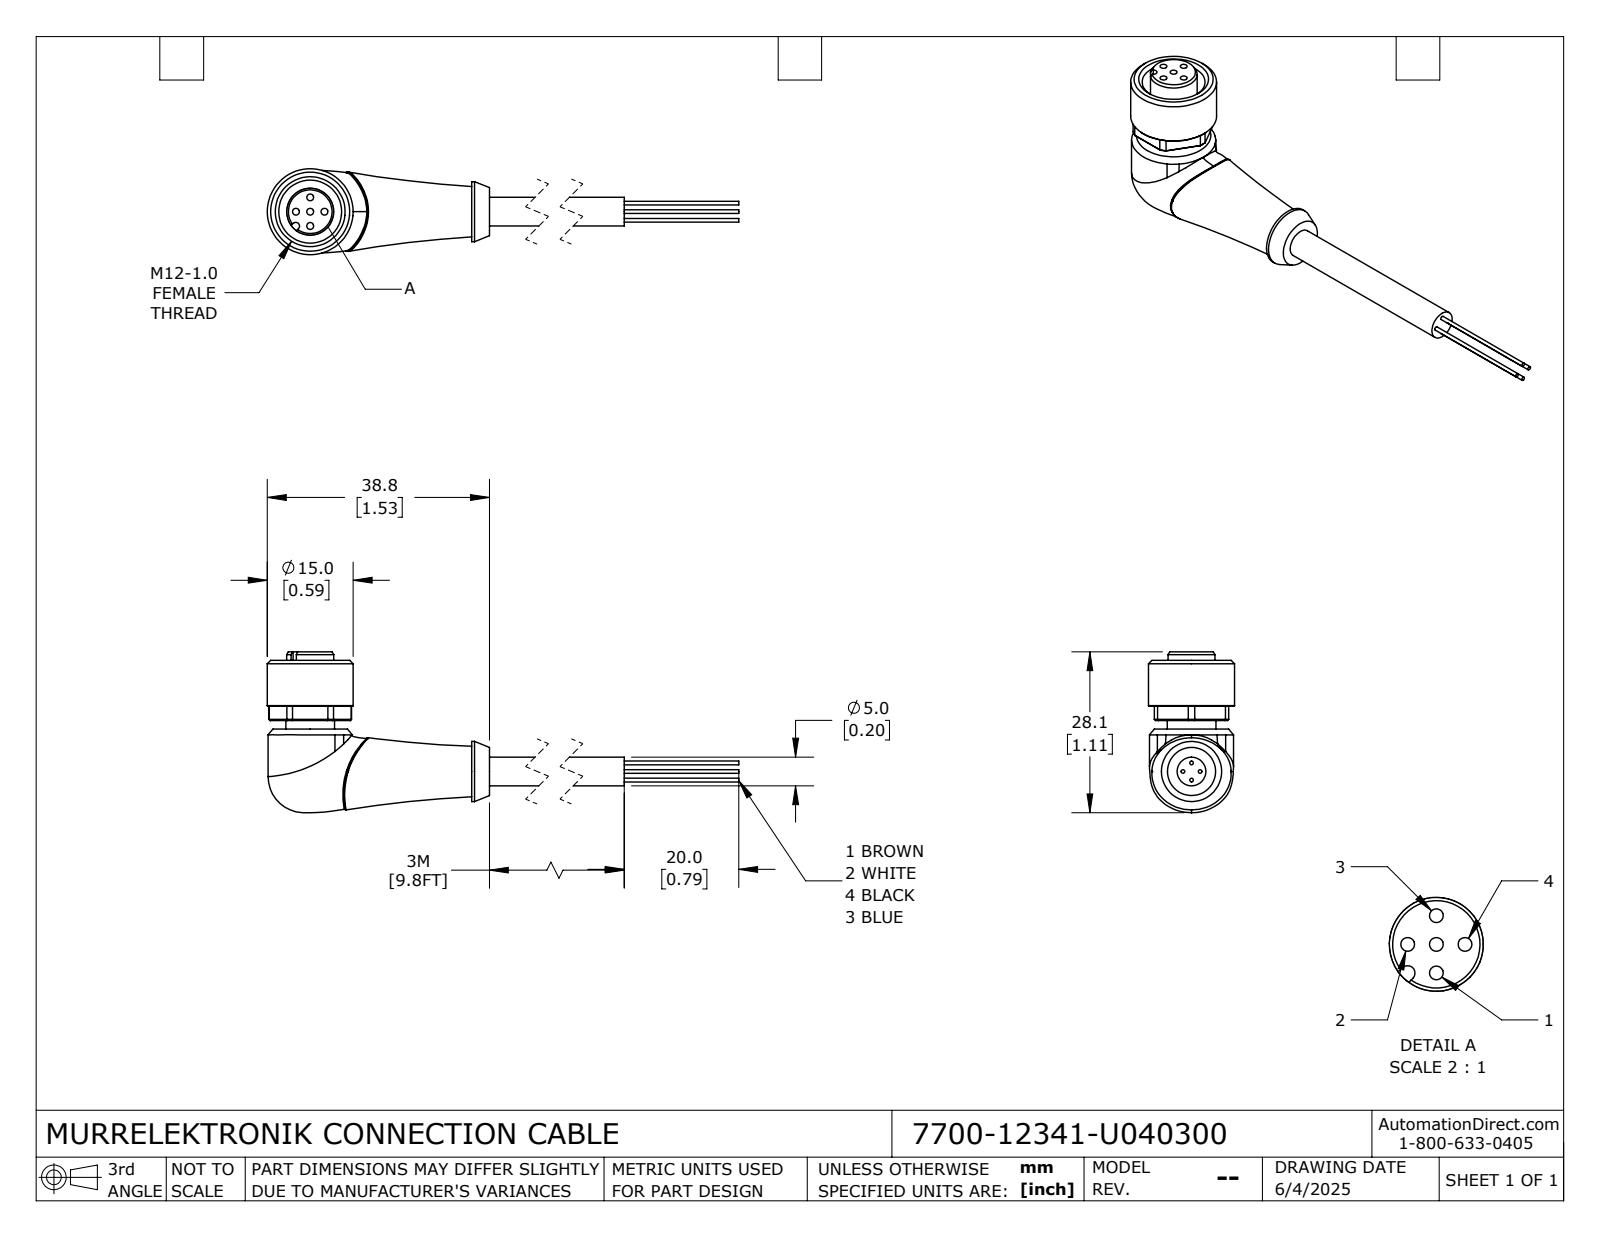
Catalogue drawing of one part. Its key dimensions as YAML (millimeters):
part_name: "7700-12341-U040300"
step_written_by: "SolidWorks 2024 (CONFIG_CONTROL_DESIGN)"
units: millimeters
bodies: {solids: 1, faces: 109, planar: 33, cylindrical: 39, other: 37}
overall_size: [93.8, 28.11, 15]
volume: 6692
surface_area: 3745
round_holes:
  - {diameter: 1.2, count: 5}
  - {diameter: 11, count: 1}
round_bosses_or_shafts:
  - {diameter: 0.64, count: 4}
  - {diameter: 15, count: 1}
  - {diameter: 10.5, count: 1}
  - {diameter: 8.5, count: 1}
  - {diameter: 8.2, count: 1}
  - {diameter: 5, count: 1}
partial_cylinders:
  - {radius: 0.65, count: 1}
  - {radius: 7.2, count: 1}
face_to_face_distances: [1.5, 12, 13, 4.5, 3, 13.5, 9, 10.5, 7.5, 2.5]
hole_center_spacings: [2.5, 3.54, 5]
